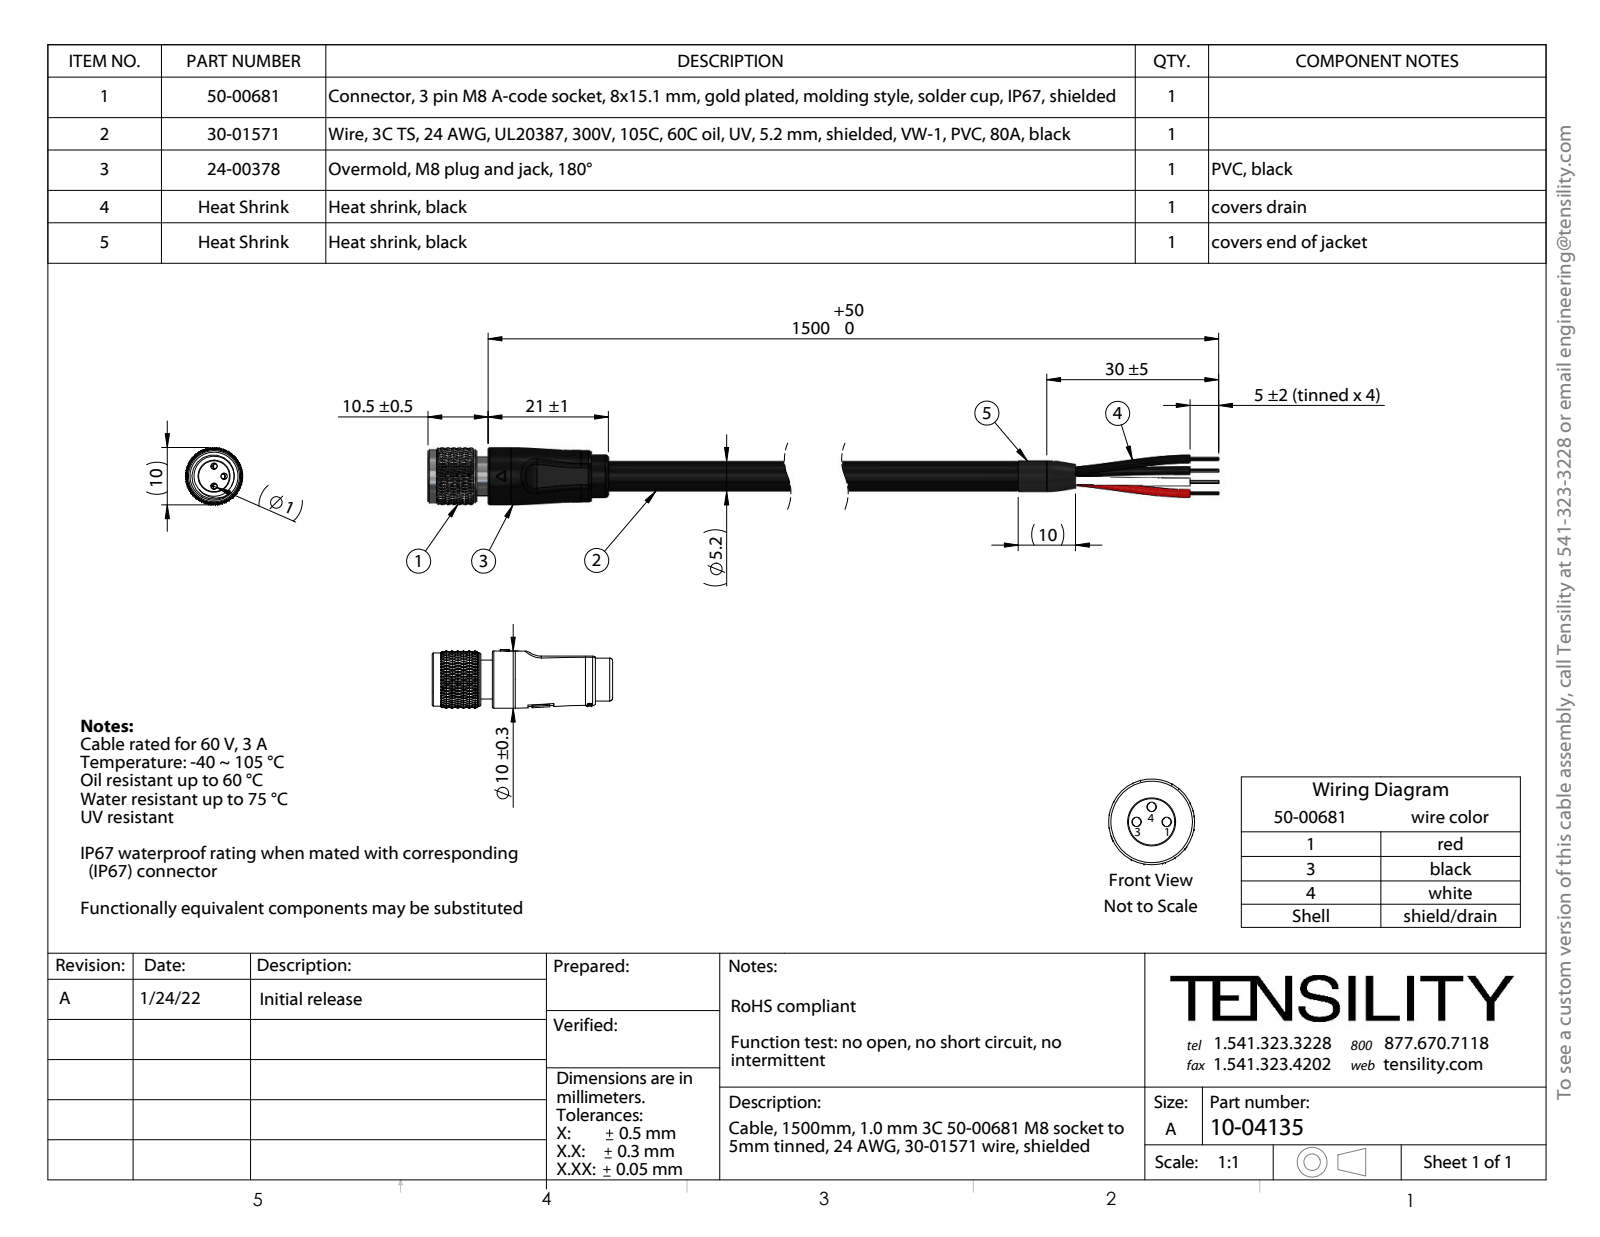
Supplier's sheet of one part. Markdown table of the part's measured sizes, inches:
| quantity | value |
| --- | --- |
| part name | 30-01571_s + t; 50-00681-02; 50-00681; 50-00681-01 (+5 more) |
| STEP written by | SolidWorks 2021 (CONFIG_CONTROL_DESIGN) |
| units | inches |
| bodies | 342 solids, 3731 faces (796 planar, 1739 cylindrical, 1196 other) |
| overall size | 8.327 × 0.404 × 0.394 |
| volume | 0.338 in³ |
| surface area | 51.08 in² |
| round holes (diameter × count) | 0.043 × 3, 0.055 × 3, 0.079 × 1, 0.143 × 1, 0.236 × 1, 0.276 × 1, 0.283 × 1, 0.323 × 1 |
| round bosses / shafts (diameter × count) | 0.059 × 3, 0.394 × 1, 0.366 × 1, 0.354 × 1, 0.299 × 1, 0.295 × 1, 0.268 × 1, 0.22 × 1 |
| partial cylindrical surfaces (radius × count) | 0.004 × 6, 0.008 × 6, 0.016 × 6, 0.028 × 2, 0.029 × 2, 0.059 × 2, 0.067 × 1, 0.068 × 1 |
| main face-to-face distances | 6.732, 0.827, 5.906, 0.197, 0.047, 0.079, 0.126, 0.02, 0.413, 1.24 |
| hole center spacings | 0.014, 0.013, 0.014, 0.015, 0.015, 0.013, 0.017, 0.039 |
